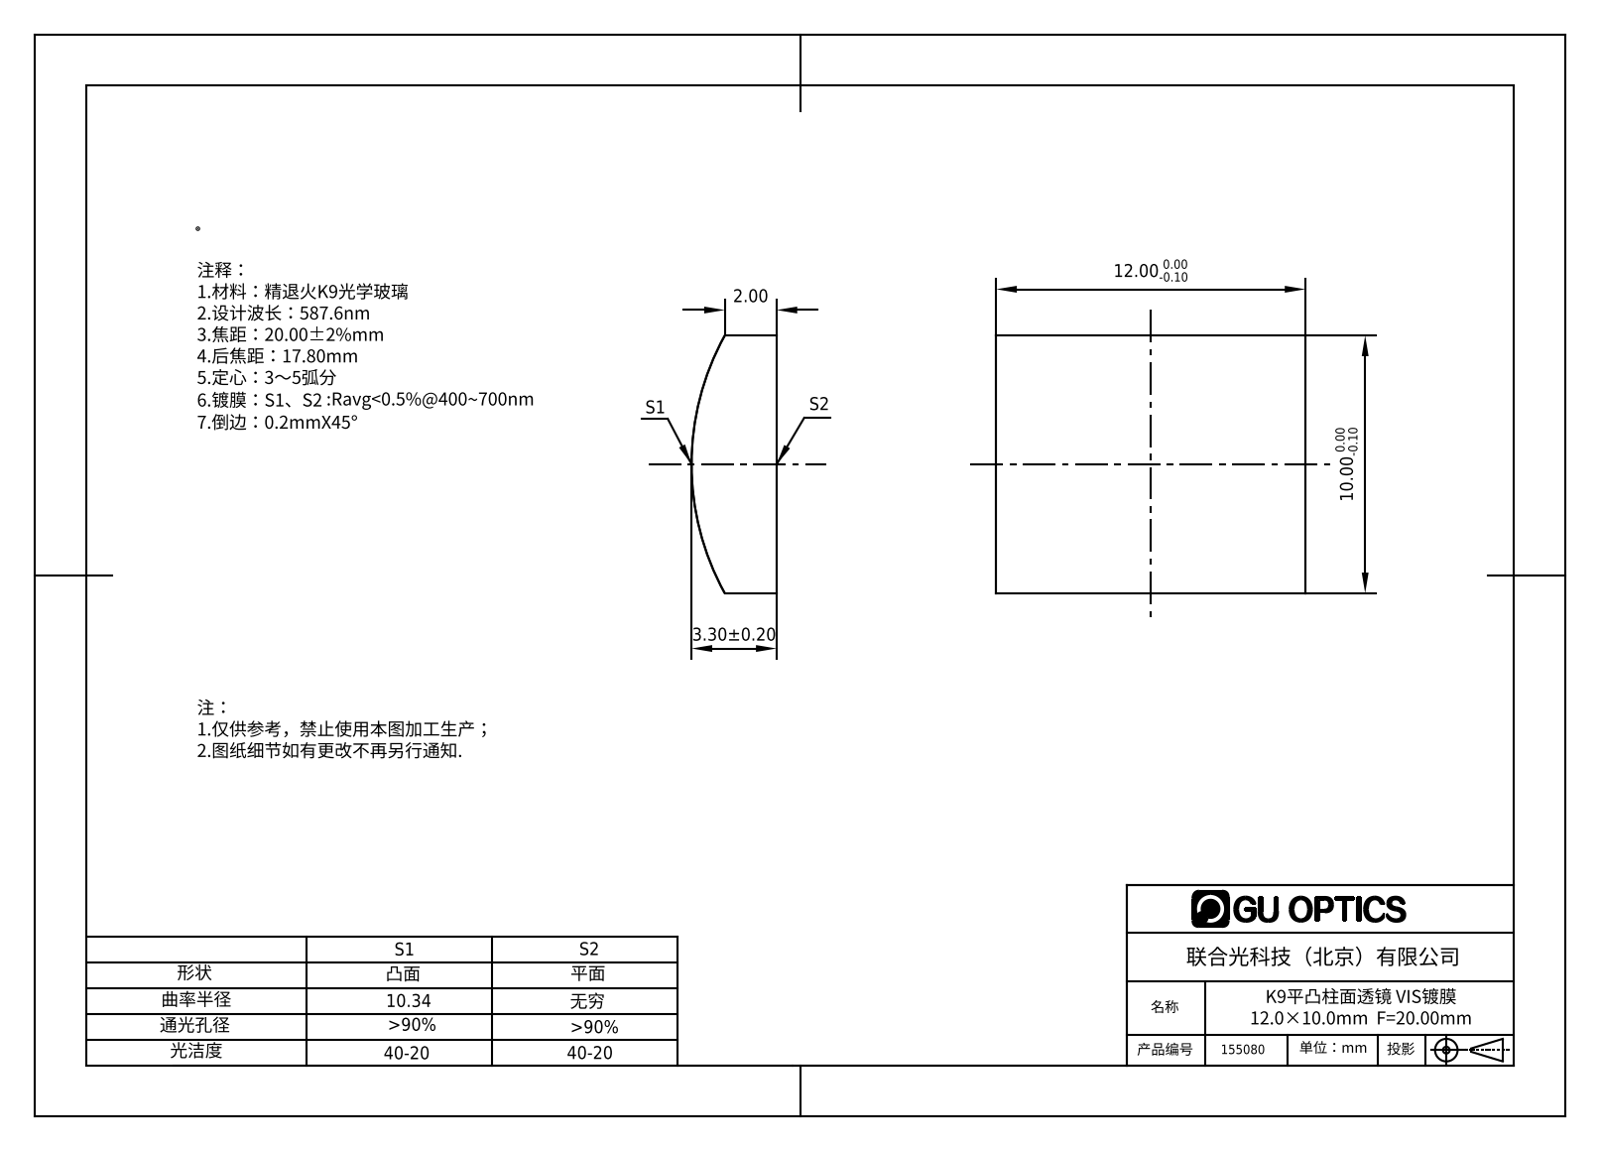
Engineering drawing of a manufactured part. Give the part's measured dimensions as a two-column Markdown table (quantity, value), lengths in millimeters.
| quantity | value |
| --- | --- |
| part name | 155014 |
| STEP written by | SolidWorks 2016 (AUTOMOTIVE_DESIGN) |
| units | millimeters |
| bodies | 1 solid, 6 faces (5 planar, 1 cylindrical, 0 other) |
| overall size | 12 × 10 × 3.3 |
| volume | 346 mm³ |
| surface area | 351 mm² |
| partial cylindrical surfaces (radius × count) | 10.34 × 1 |
| main face-to-face distances | 12, 10 |
